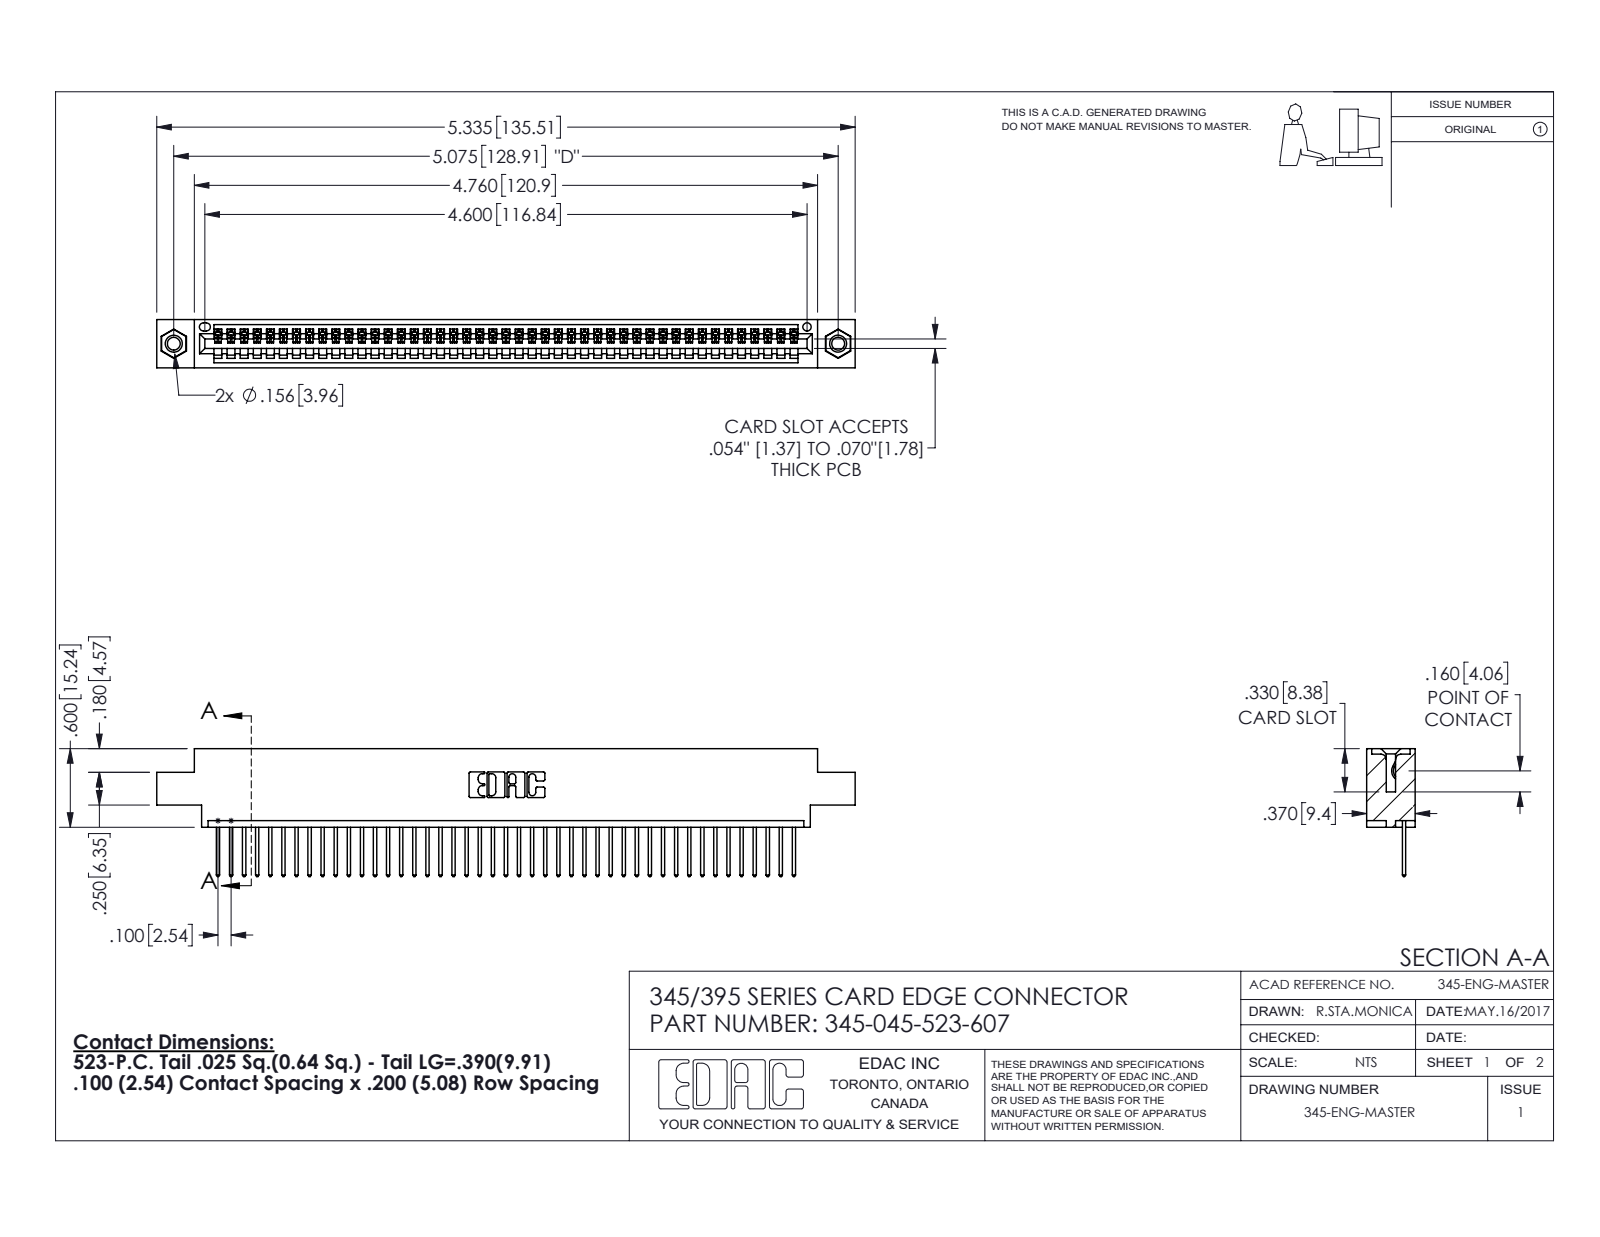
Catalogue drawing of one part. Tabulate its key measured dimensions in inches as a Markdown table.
| quantity | value |
| --- | --- |
| part name | 345-045-523-607; 345-250-001_345-250-005-103; 345 Part_0.170 Offset - 0.156 Dia-TI; 345-292-001_345-293-123 |
| STEP written by | SolidWorks 2016 (CONFIG_CONTROL_DESIGN) |
| units | inches |
| bodies | 48 solids, 2800 faces (1916 planar, 868 cylindrical, 16 other) |
| overall size | 5.335 × 0.977 × 0.37 |
| volume | 0.778 in³ |
| surface area | 26.65 in² |
| round holes (diameter × count) | 0.098 × 2, 0.125 × 2, 0.156 × 2, 0.064 × 1 |
| round bosses / shafts (diameter × count) | 0.155 × 2 |
| partial cylindrical surfaces (radius × count) | 0.006 × 90, 0.01 × 90, 0.01 × 22, 0.007 × 6, 0.031 × 6, 0.026 × 3, 0.031 × 2, 0.04 × 2 |
| main face-to-face distances | 0.072, 0.298, 0.37, 0.2, 0.098, 0.272, 0.025, 0.225, 0.175, 0.149 |
| hole center spacings | 0.27, 4.839, 5.075 |
